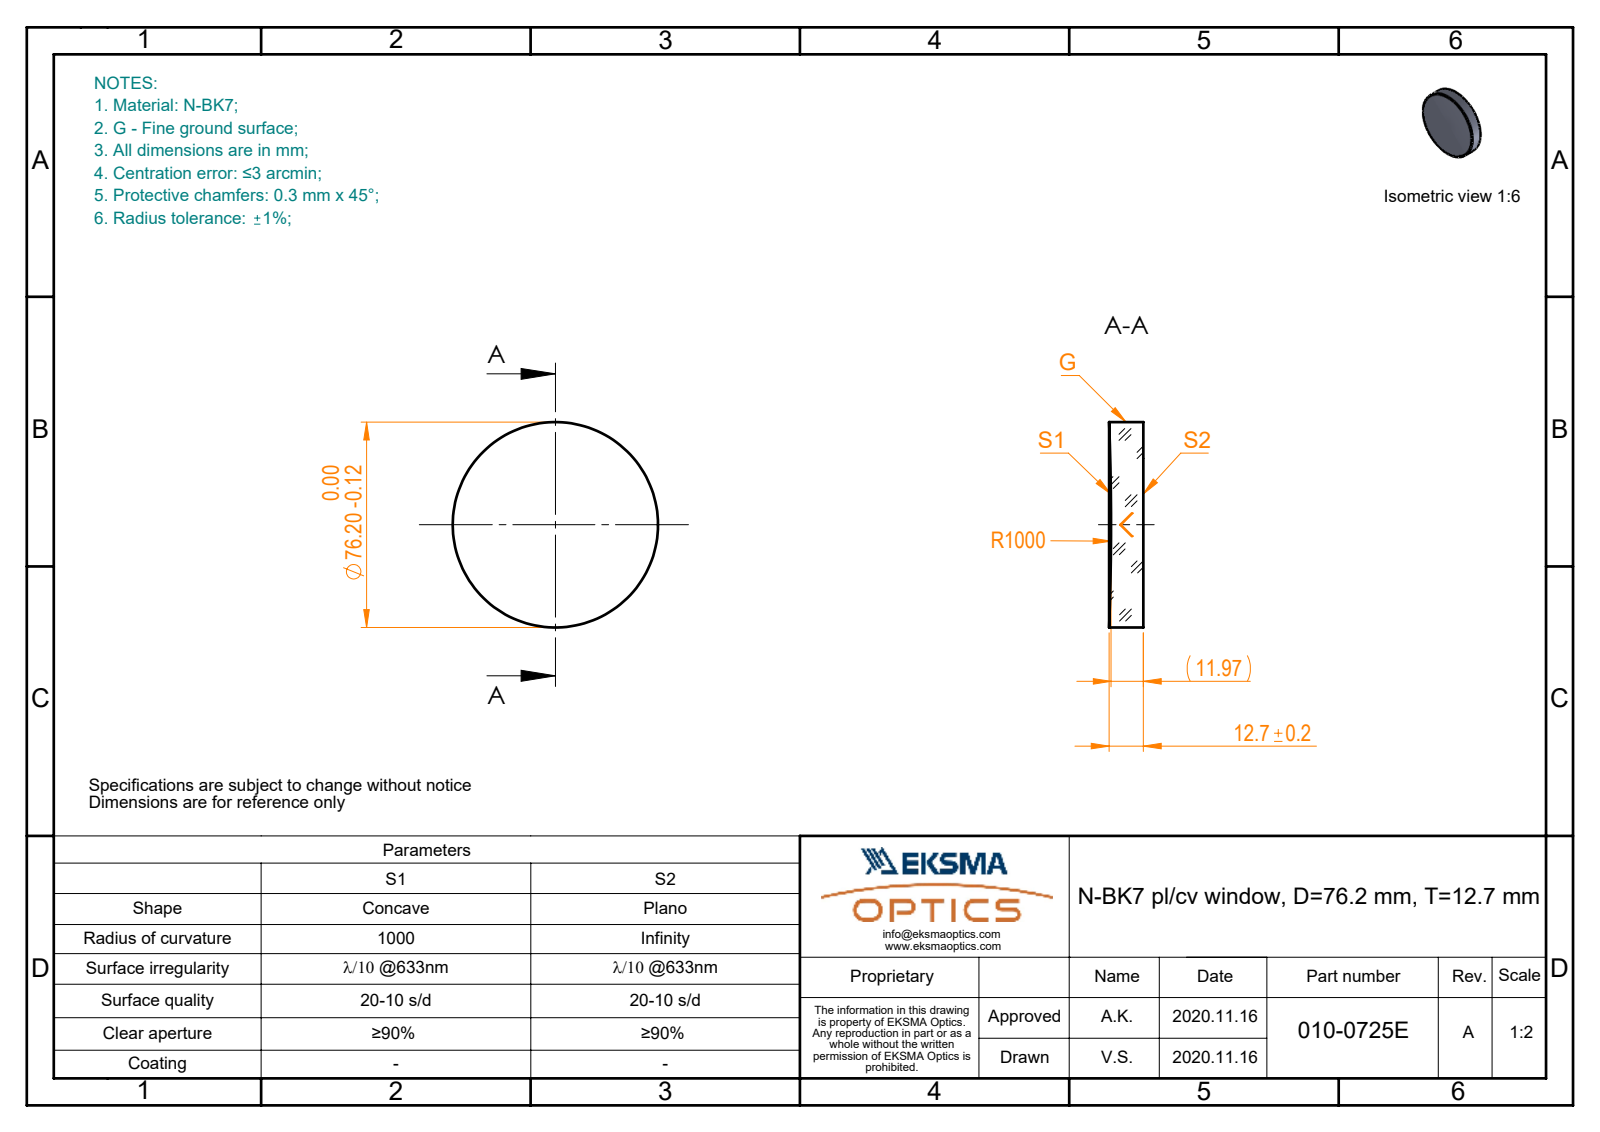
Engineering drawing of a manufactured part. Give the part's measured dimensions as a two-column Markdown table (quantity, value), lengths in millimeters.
| quantity | value |
| --- | --- |
| part name | 010-0725E_N-BK7_PCV_window |
| STEP written by | SolidWorks 2019 (CONFIG_CONTROL_DESIGN) |
| units | millimeters |
| bodies | 1 solid, 5 faces (1 planar, 2 cylindrical, 2 other) |
| overall size | 76.2 × 76.2 × 12.7 |
| volume | 56 261 mm³ |
| surface area | 12 163 mm² |
| round bosses / shafts (diameter × count) | 76.2 × 1 |
